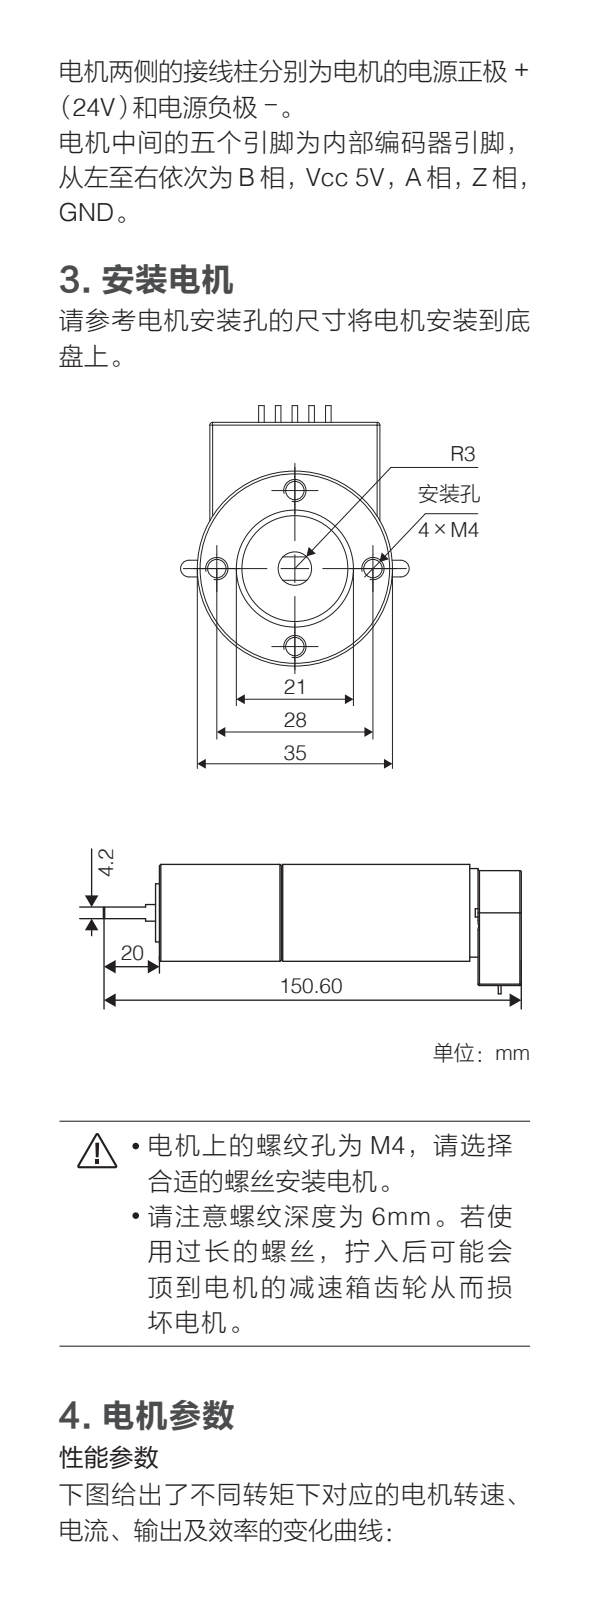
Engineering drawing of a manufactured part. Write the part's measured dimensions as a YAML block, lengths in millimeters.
step_written_by: "SolidWorks 2016 (CONFIG_CONTROL_DESIGN)"
units: millimeters
bodies: {solids: 0, faces: 204, planar: 107, cylindrical: 70, other: 27}
overall_size: [152.58, 42.8, 36.8]
round_holes:
  - {diameter: 4, count: 4}
  - {diameter: 2.5, count: 2}
  - {diameter: 13, count: 1}
round_bosses_or_shafts:
  - {diameter: 2.5, count: 4}
  - {diameter: 35, count: 1}
  - {diameter: 34.8, count: 1}
  - {diameter: 34.7, count: 1}
  - {diameter: 32, count: 1}
  - {diameter: 20, count: 1}
  - {diameter: 7.8, count: 1}
partial_cylinders:
  - {radius: 1, count: 13}
  - {radius: 2, count: 6}
  - {radius: 2.5, count: 2}
  - {radius: 3.1, count: 1}
  - {radius: 12.5, count: 1}
  - {radius: 14.9, count: 1}
face_to_face_distances: [29.8, 132.48, 111.98, 20.5, 2, 3, 135.48, 5, 114.98, 22.5]
hole_center_spacings: [14, 19.79, 6.13, 15.9, 16.68, 24.88, 27.99, 29.32]
